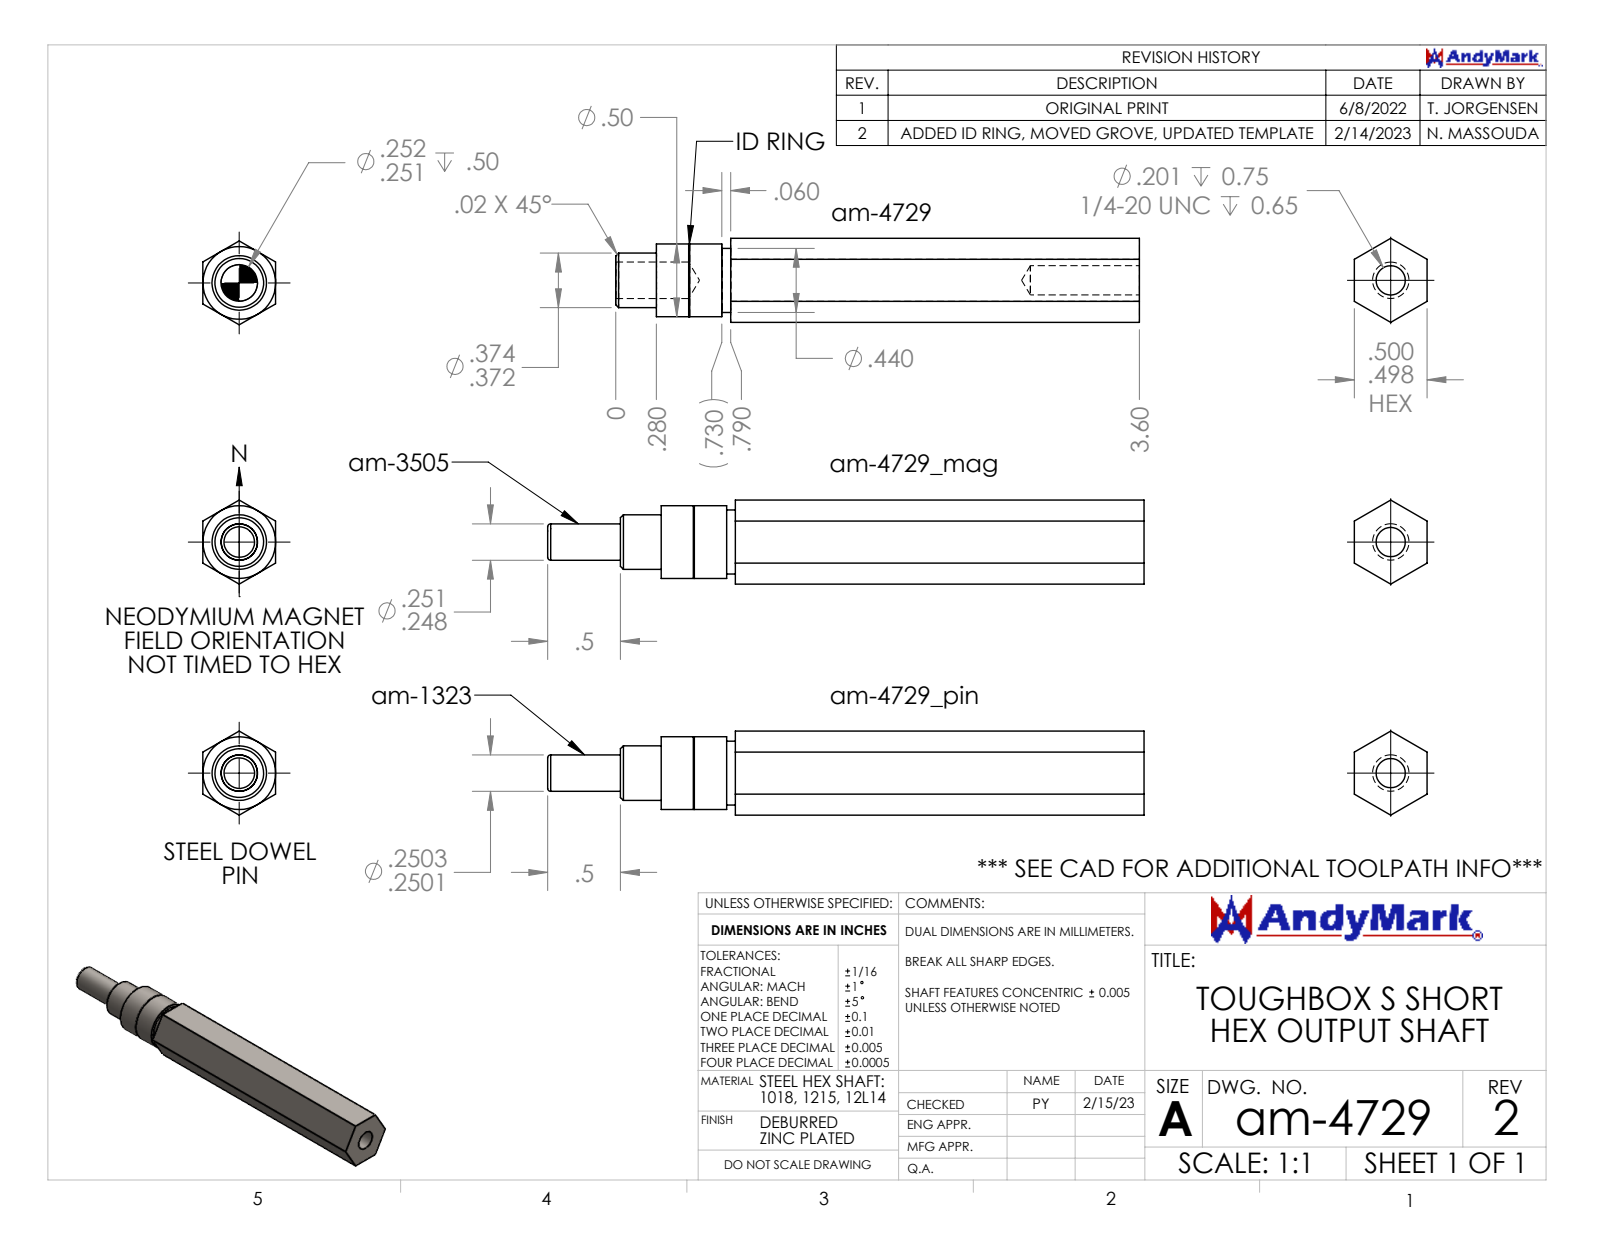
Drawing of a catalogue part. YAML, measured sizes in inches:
part_name: "am-4729 ToughBox S Short Hex Output Shaft"
step_written_by: "SolidWorks 2022 (CONFIG_CONTROL_DESIGN)"
units: inches
bodies: {solids: 1, faces: 33, planar: 11, cylindrical: 12, other: 10}
overall_size: [3.6, 0.577, 0.5]
volume: 0.686
surface_area: 7.382
round_holes:
  - {diameter: 0.201, count: 1}
  - {diameter: 0.251, count: 1}
round_bosses_or_shafts:
  - {diameter: 0.5, count: 1}
  - {diameter: 0.44, count: 1}
  - {diameter: 0.375, count: 1}
face_to_face_distances: [0.5, 3.32, 0.51, 2.81, 0.45, 0.06, 2.87, 0.28, 0.73, 0.79]
